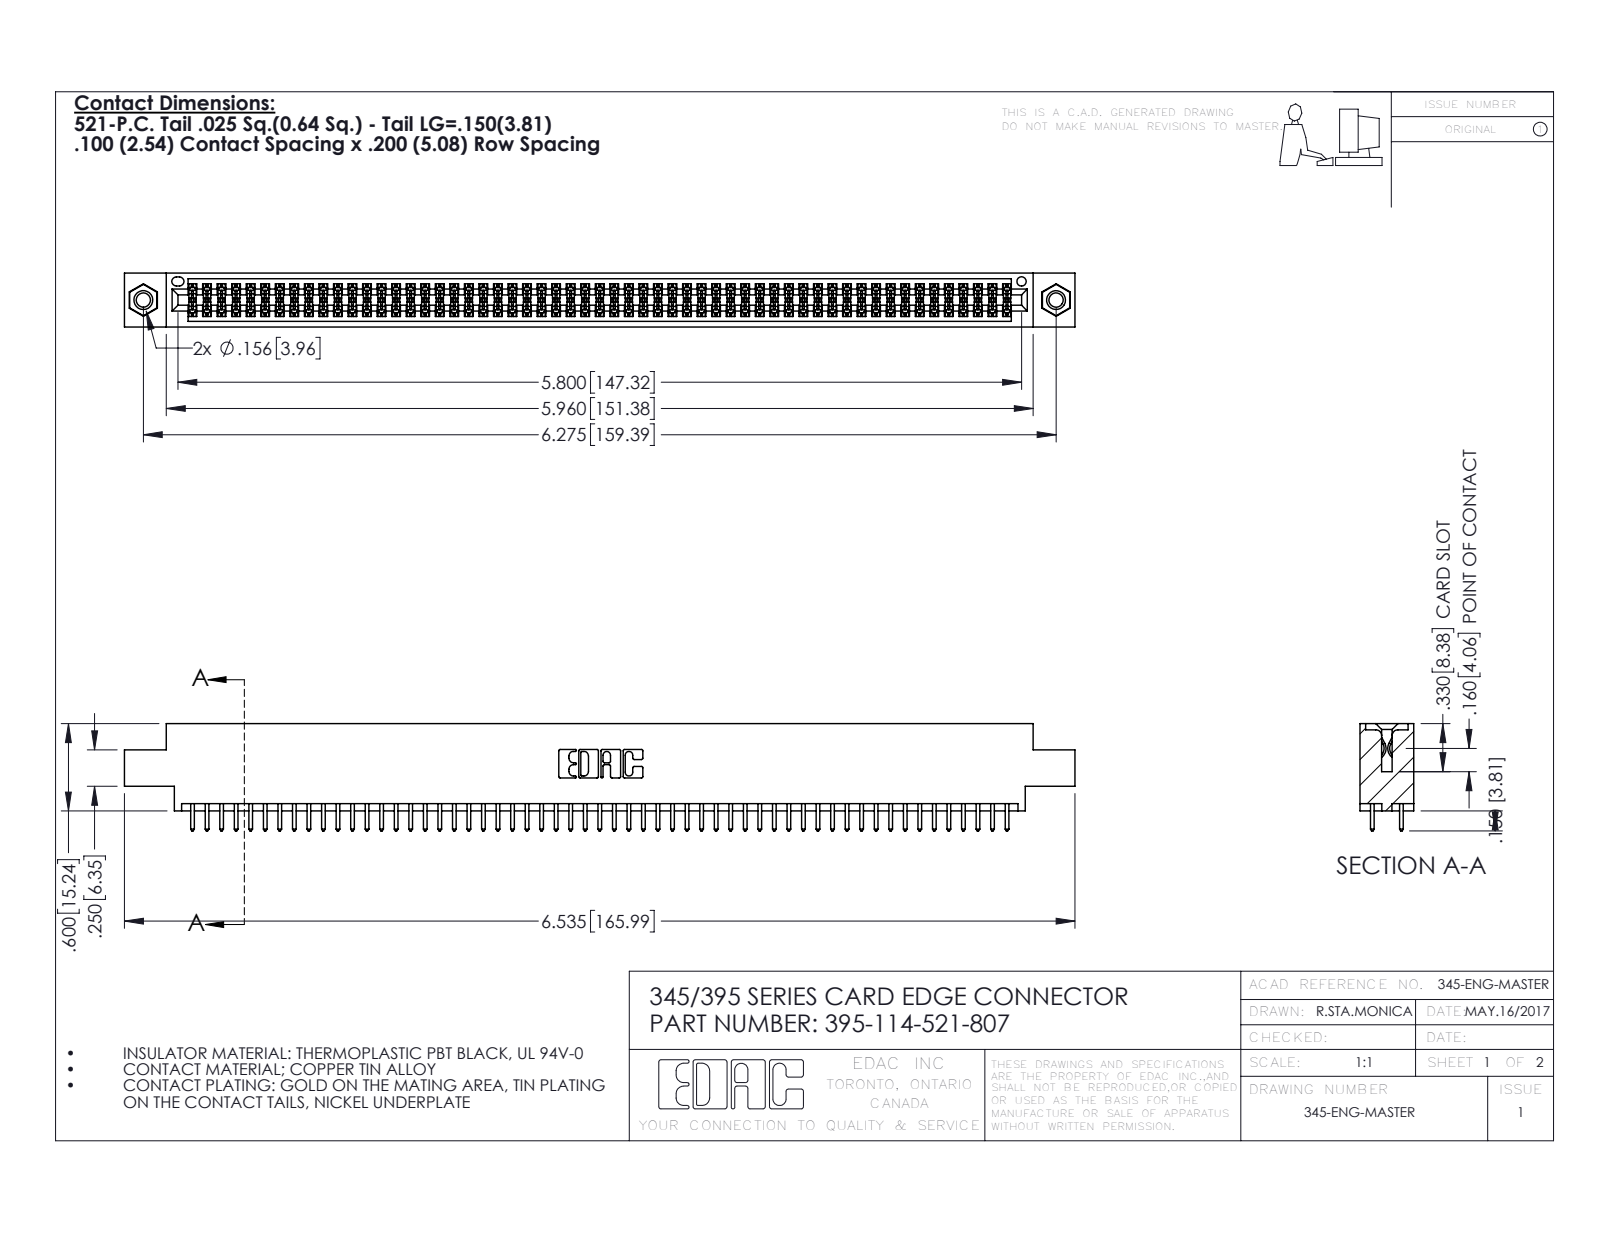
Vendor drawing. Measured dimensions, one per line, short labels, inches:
name: 345-250-001_345-250-005-103; 345 Part_0.170 Offset - 0.156 Dia-TI; 395-114-521-807; 345-292-001_345-293-121
written by: SolidWorks 2016 (CONFIG_CONTROL_DESIGN)
unit: in
bodies: 117 solids, 5890 faces (3878 planar, 1996 cylindrical, 16 other)
size: 6.535 × 0.737 × 0.37
volume: 0.982 in³; area: 37.11 in²
holes: 2× ⌀0.098, 2× ⌀0.125, 2× ⌀0.156, 1× ⌀0.064
bosses: 2× ⌀0.155
rounds: 171× R0.006, 114× R0.01, 22× R0.01, 6× R0.007, 6× R0.031, 3× R0.026, 2× R0.014, 2× R0.019
face distances: 0.072, 0.298, 0.2, 0.37, 0.098, 0.272, 0.025, 0.225, 0.175, 0.149
hole spacings: 0.27, 6.039, 6.275
